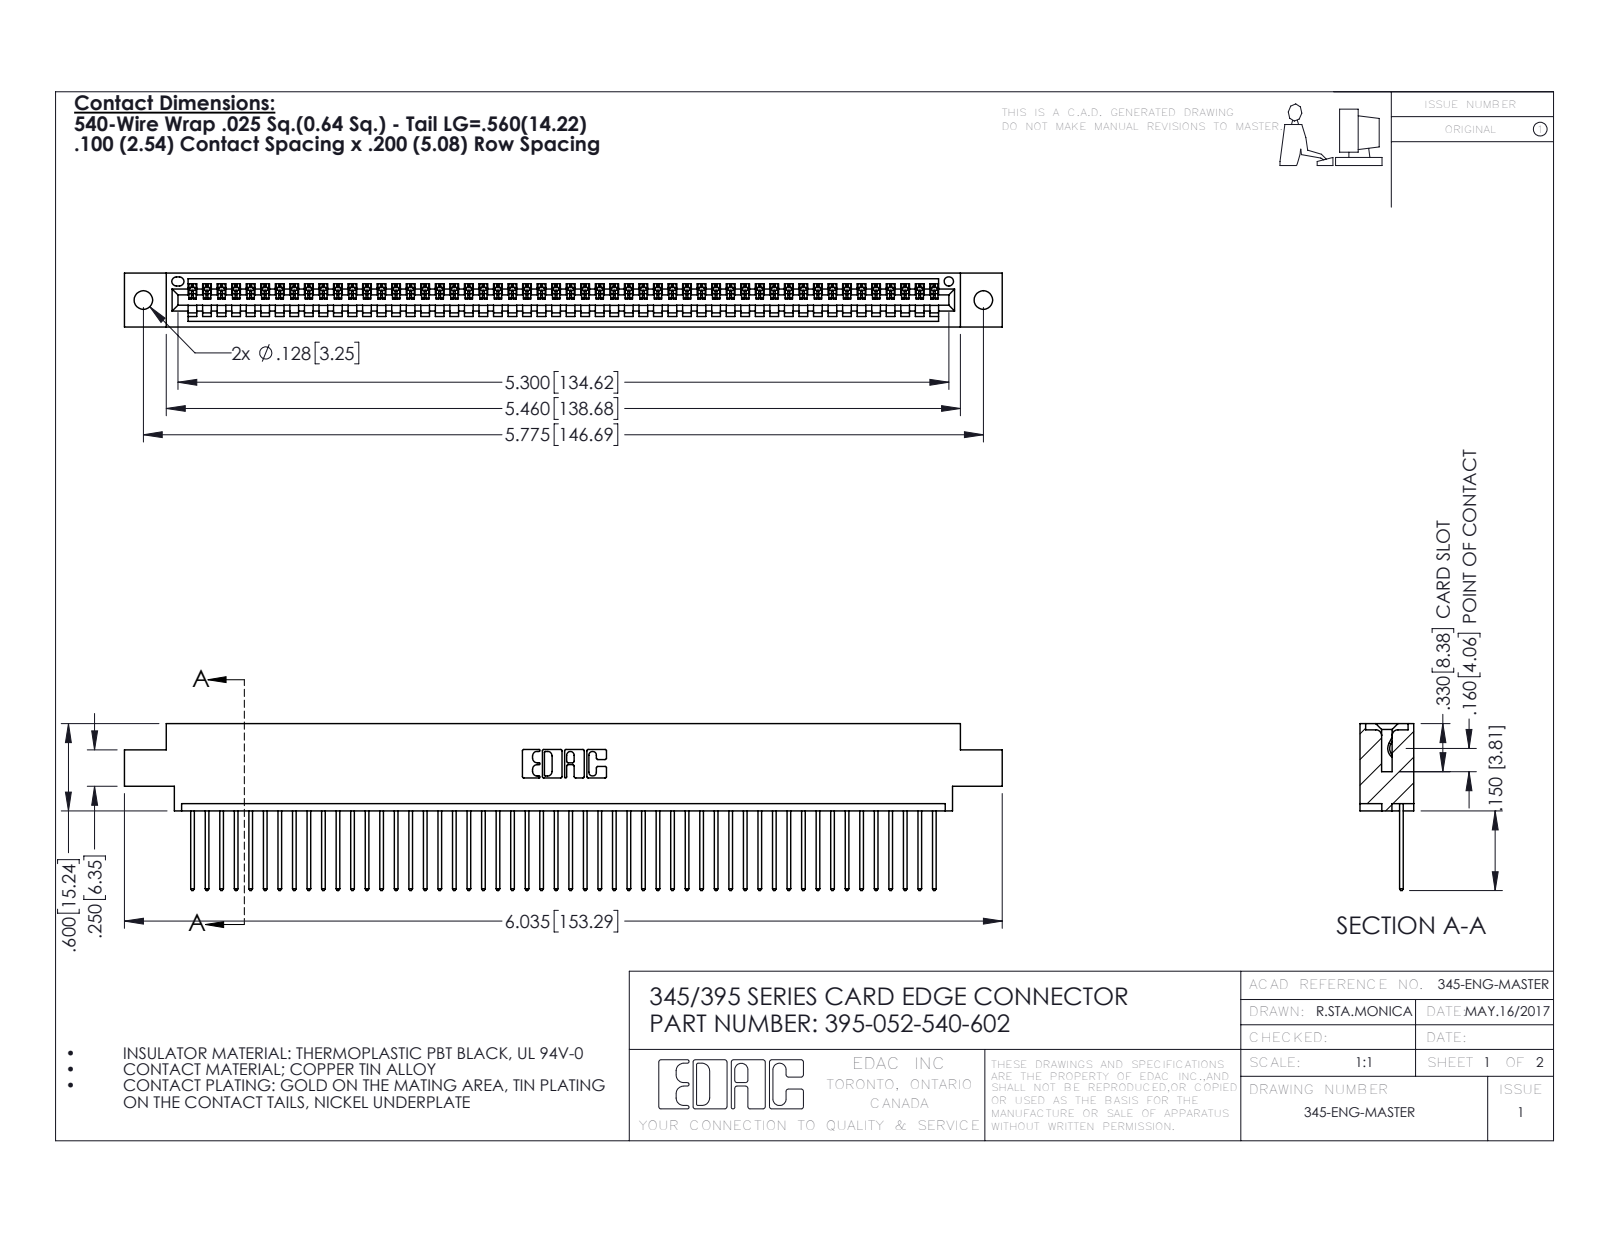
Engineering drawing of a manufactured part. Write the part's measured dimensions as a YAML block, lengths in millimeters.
part_name: "395-052-540-602; 345-292-001_345-293-140; 345 Part_0.170 Offset - 0.128 Dia"
step_written_by: "SolidWorks 2016 (CONFIG_CONTROL_DESIGN)"
units: millimeters
bodies: {solids: 53, faces: 3146, planar: 2164, cylindrical: 982, other: 0}
overall_size: [153.3, 29.1, 9.4]
volume: 14600
surface_area: 19850
round_holes:
  - {diameter: 3.3, count: 2}
  - {diameter: 1.6, count: 1}
partial_cylinders:
  - {radius: 0.2, count: 104}
  - {radius: 0.3, count: 104}
  - {radius: 0.3, count: 22}
  - {radius: 0.2, count: 6}
  - {radius: 0.8, count: 6}
  - {radius: 0.7, count: 3}
  - {radius: 0.8, count: 2}
  - {radius: 1, count: 2}
face_to_face_distances: [7.6, 1.8, 9.4, 2.5, 6.9, 0.6, 5.1, 5.7, 4.4, 3.8]
hole_center_spacings: [6.9, 140.7, 146.7]
